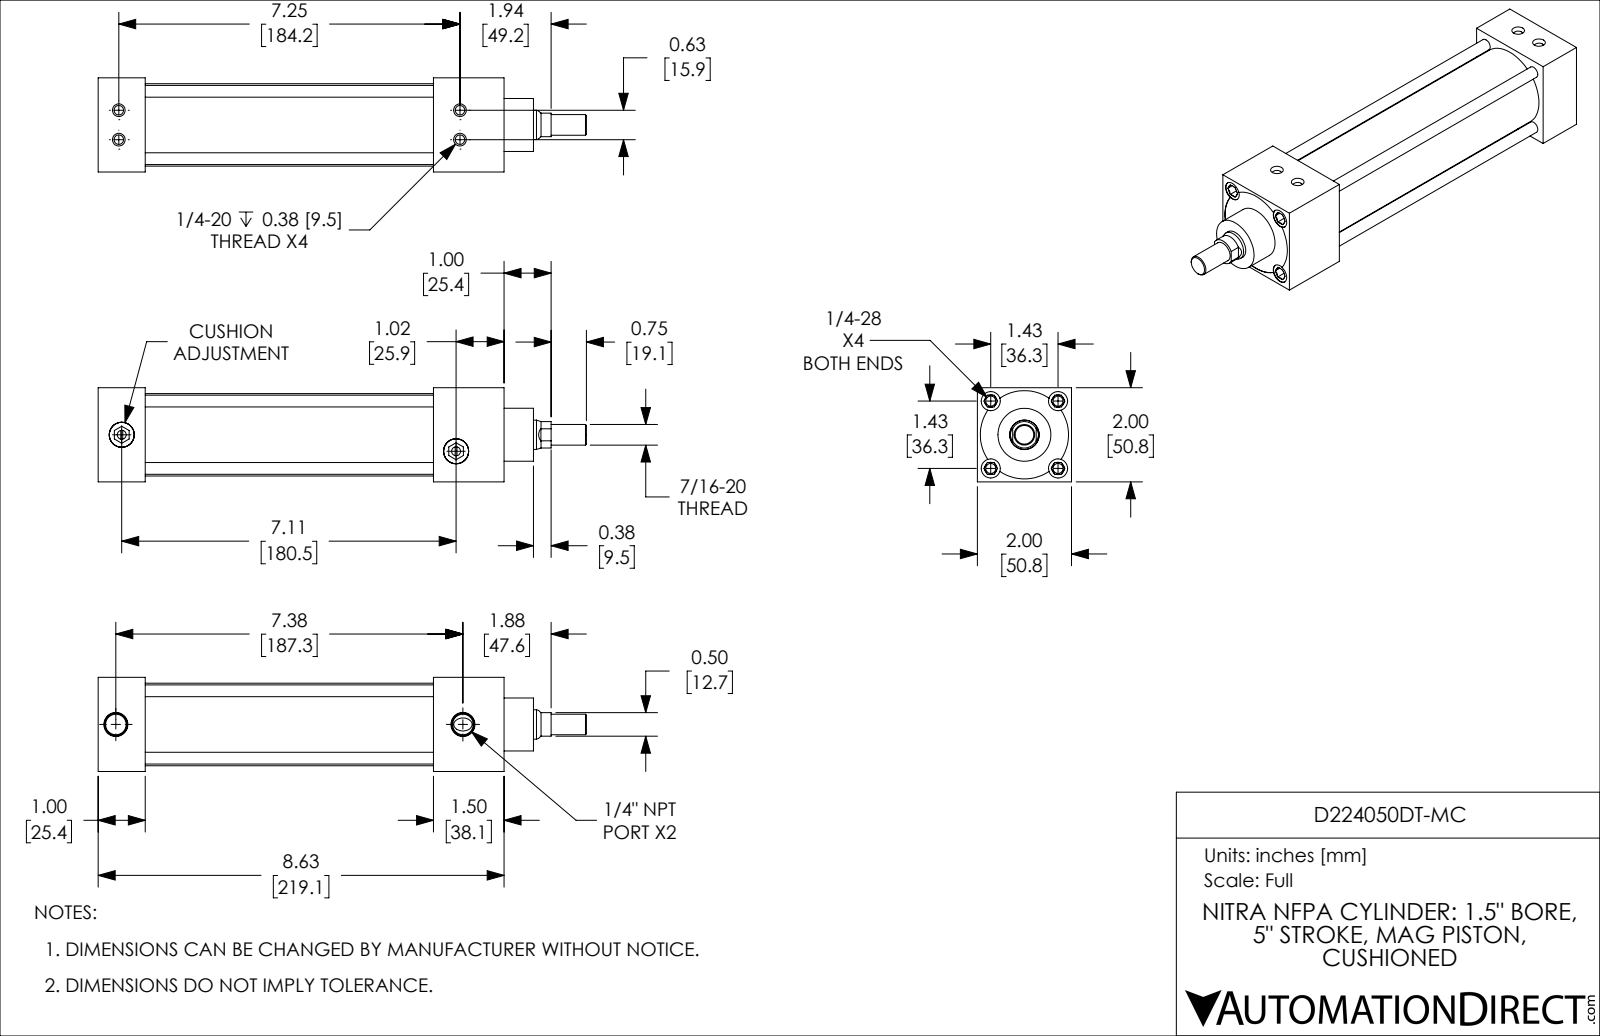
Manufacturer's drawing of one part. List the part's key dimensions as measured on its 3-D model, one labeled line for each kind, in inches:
Part name (STEP PRODUCT): D224050DT-MC_PISTON_KK1; D224050DT-MC; D224050DT-MC_BODY; D224050DT-MC_CUSHION
STEP written by: SolidWorks 2019 (CONFIG_CONTROL_DESIGN)
Units: inches
Bodies: 4 solids, 251 faces (90 planar, 81 cylindrical, 80 other)
Overall size (bounding box): 10.375 × 2 × 2
Volume: 18.88 in³ · Surface area: 155.5 in²
Round holes (diameter × count): ⌀0.201 ×4, ⌀0.213 ×4, ⌀0.406 ×4, ⌀0.19 ×2, ⌀0.438 ×2, ⌀0.531 ×2, ⌀0.626 ×1, ⌀1.501 ×1
Round bosses / shafts (diameter × count): ⌀0.25 ×4, ⌀0.532 ×2, ⌀1.751 ×1, ⌀1.499 ×1, ⌀1.125 ×1, ⌀0.624 ×1, ⌀0.437 ×1
Partial cylindrical surfaces — rounded edges, fillets, slot ends (radius × count): R0.281 ×1, R0.937 ×1
Main face-to-face distances: 2, 1, 7.125, 6.125, 8.62, 7.62, 1.495, 1.125, 2.125, 5
Hole centre spacings: 0.319, 1.011, 1.43, 0.625, 2.022, 7.25, 7.277, 7.319
